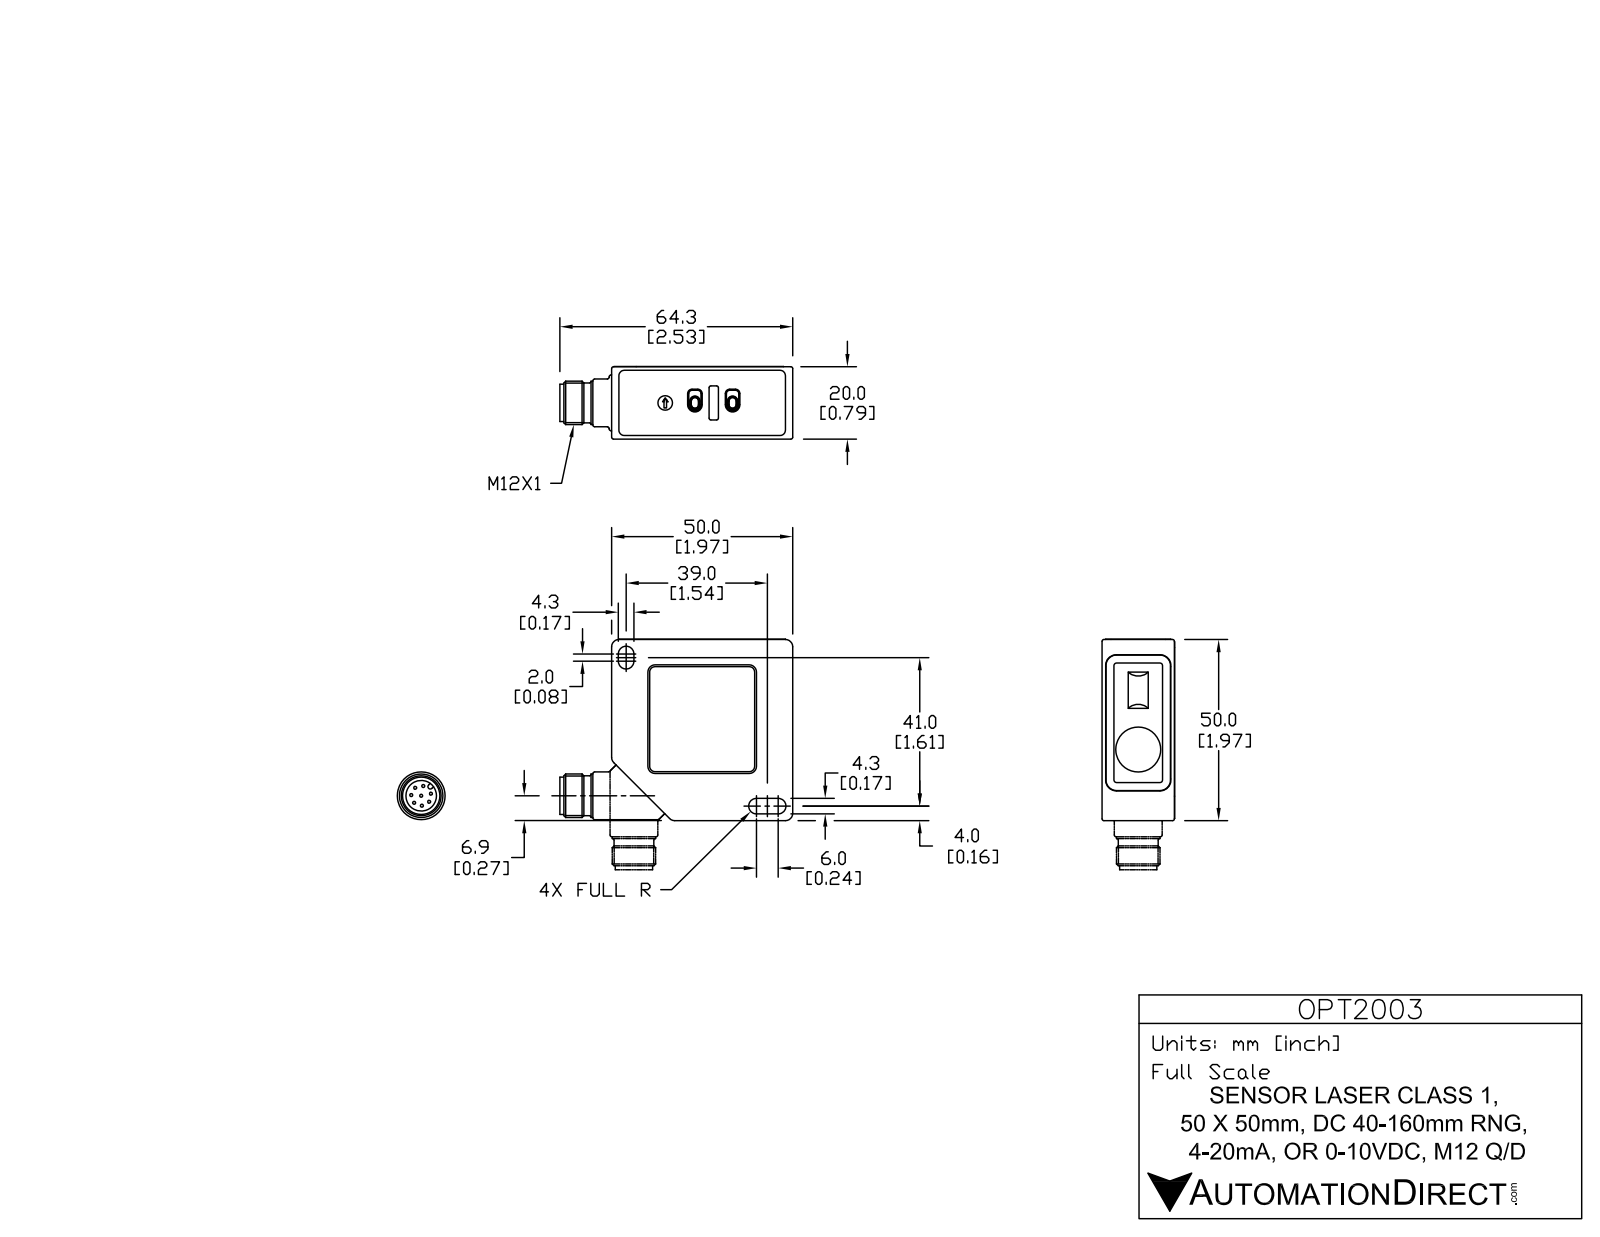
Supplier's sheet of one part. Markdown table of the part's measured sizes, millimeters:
| quantity | value |
| --- | --- |
| part name | OPT2003 |
| STEP written by | SolidWorks 2013 (AUTOMOTIVE_DESIGN) |
| units | millimeters |
| bodies | 15 solids, 301 faces (153 planar, 134 cylindrical, 14 other) |
| overall size | 64.43 × 50.1 × 20 |
| volume | 48 653 mm³ |
| surface area | 16 026 mm² |
| round holes (diameter × count) | 4 × 1, 8.45 × 1 |
| round bosses / shafts (diameter × count) | 0.82 × 8, 18 × 1, 13.5 × 1, 12.39 × 1, 12 × 1, 11 × 1, 10.3 × 1 |
| partial cylindrical surfaces (radius × count) | 2 × 17, 0.2 × 10, 1 × 8, 2.1 × 5, 0.5 × 4, 1.2 × 4, 2.15 × 4, 2.9 × 4 |
| main face-to-face distances | 20, 19.8, 50, 50.1, 48.3, 1.6, 48.4, 5.33, 53.63, 53.73 |
